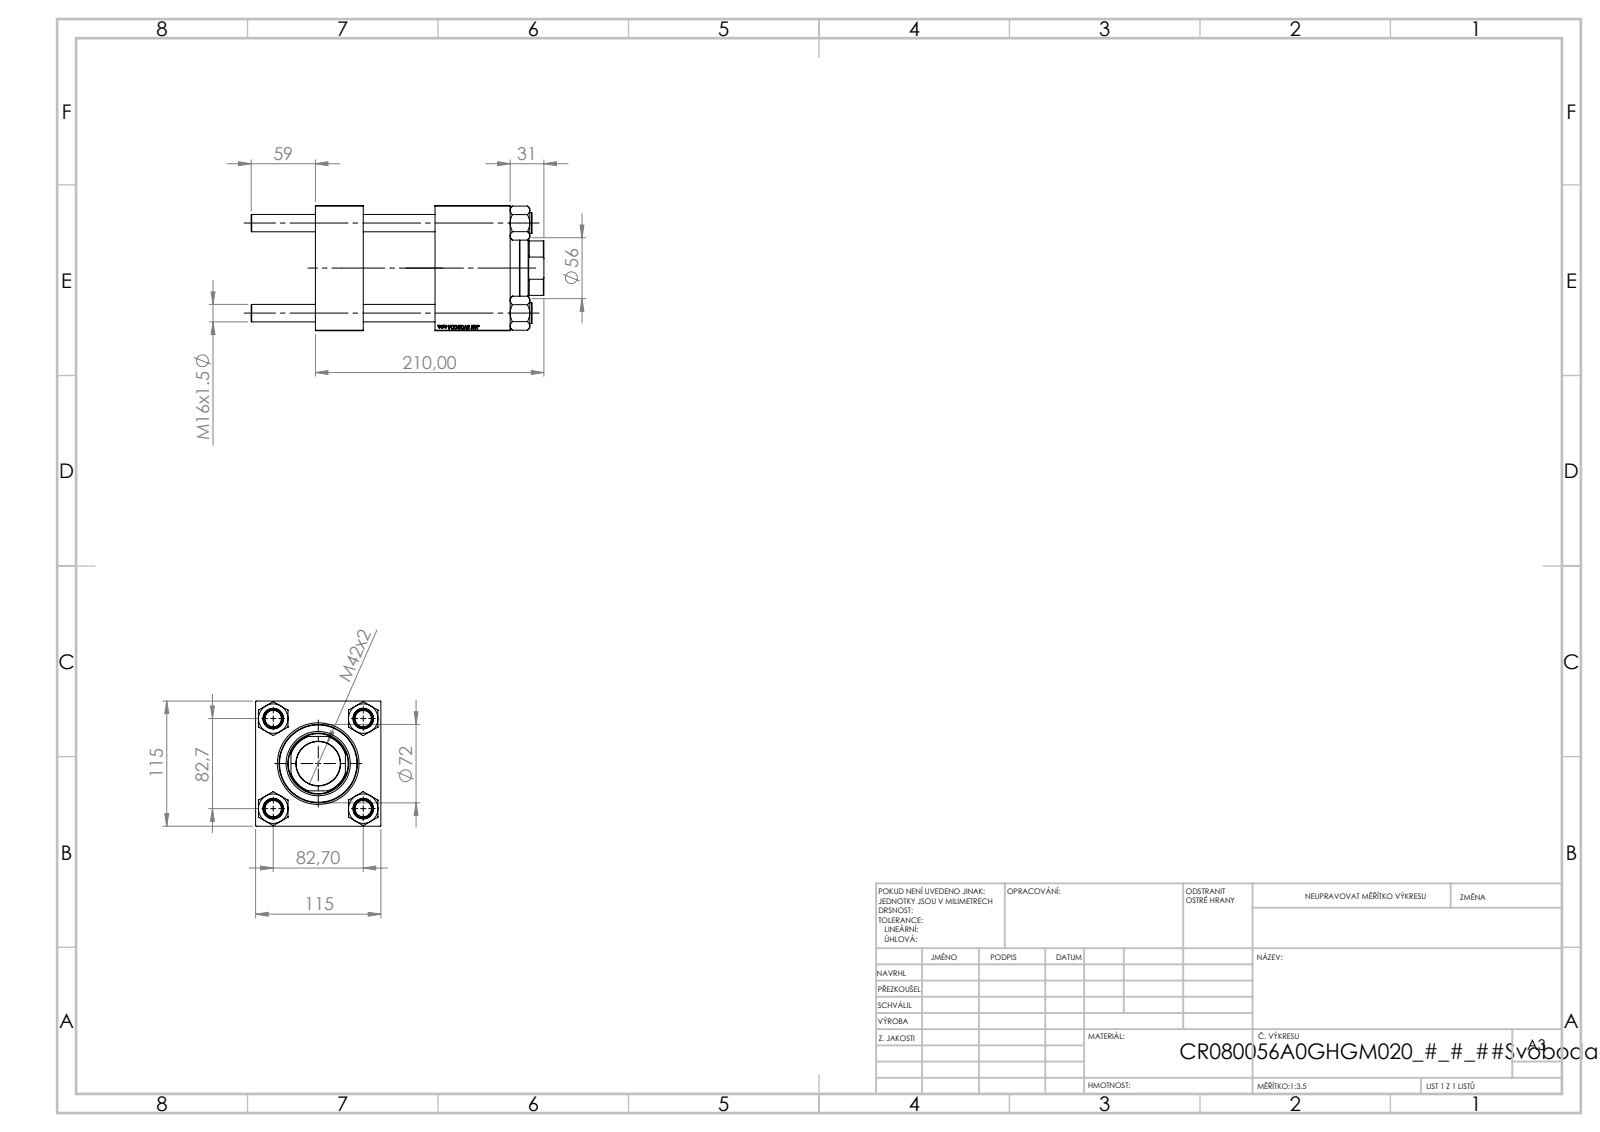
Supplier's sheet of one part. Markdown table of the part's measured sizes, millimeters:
| quantity | value |
| --- | --- |
| part name | NUT_M5; V215CR_BODY_A; CR025_012_A_0_G_A_G_M_020_+#_##_TYCINKA; V215_VC_A (+1 more) |
| STEP written by | SolidWorks 2019 (CONFIG_CONTROL_DESIGN) |
| units | millimeters |
| bodies | 11 solids, 1179 faces (567 planar, 76 cylindrical, 536 other) |
| overall size | 269 × 115 × 115 |
| volume | 1 941 000 mm³ |
| surface area | 306 376 mm² |
| round holes (diameter × count) | 16 × 4, 7 × 2, 26.44 × 2, 35 × 2, 40.5 × 1, 56 × 1, 59 × 1, 61 × 1, 72 × 1, 80 × 1 |
| round bosses / shafts (diameter × count) | 19 × 4, 86 × 1 |
| partial cylindrical surfaces (radius × count) | 27 × 1 |
| main face-to-face distances | 115, 44, 179, 135, 110, 66, 69, 20, 89, 150.3 |
| hole center spacings | 58.48, 82.7, 116.96, 111 |
